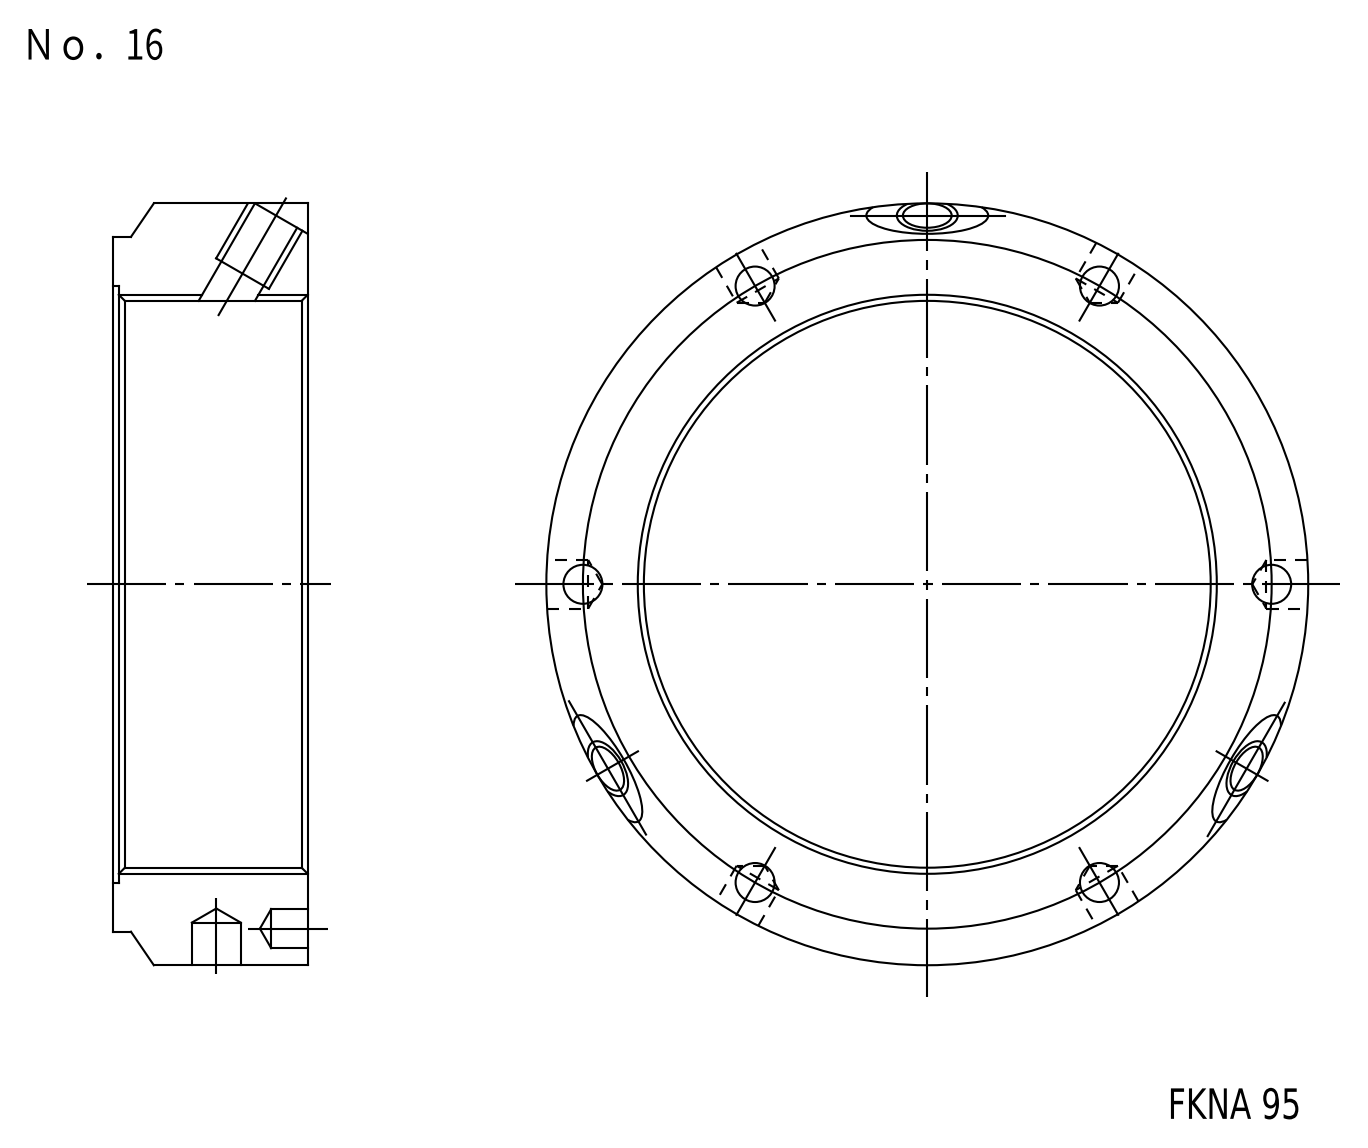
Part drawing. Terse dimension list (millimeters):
name: FKD FKNA95
written by: Autodesk Inventor LT (CONFIG_CONTROL_DESIGN)
unit: mm
bodies: 1 solid, 44 faces (6 planar, 25 cylindrical, 13 other)
size: 125 × 125 × 32
volume: 152 965 mm³; area: 33 780 mm²
holes: 6× ⌀6.4, 3× ⌀8, 3× ⌀8.38, 3× ⌀10.2, 1× ⌀95, 1× ⌀98
bosses: 1× ⌀125, 1× ⌀114
rounds: 3× R20
face distances: 32, 1.5, 30.5
hole spacings: 56.5, 97.86, 113
